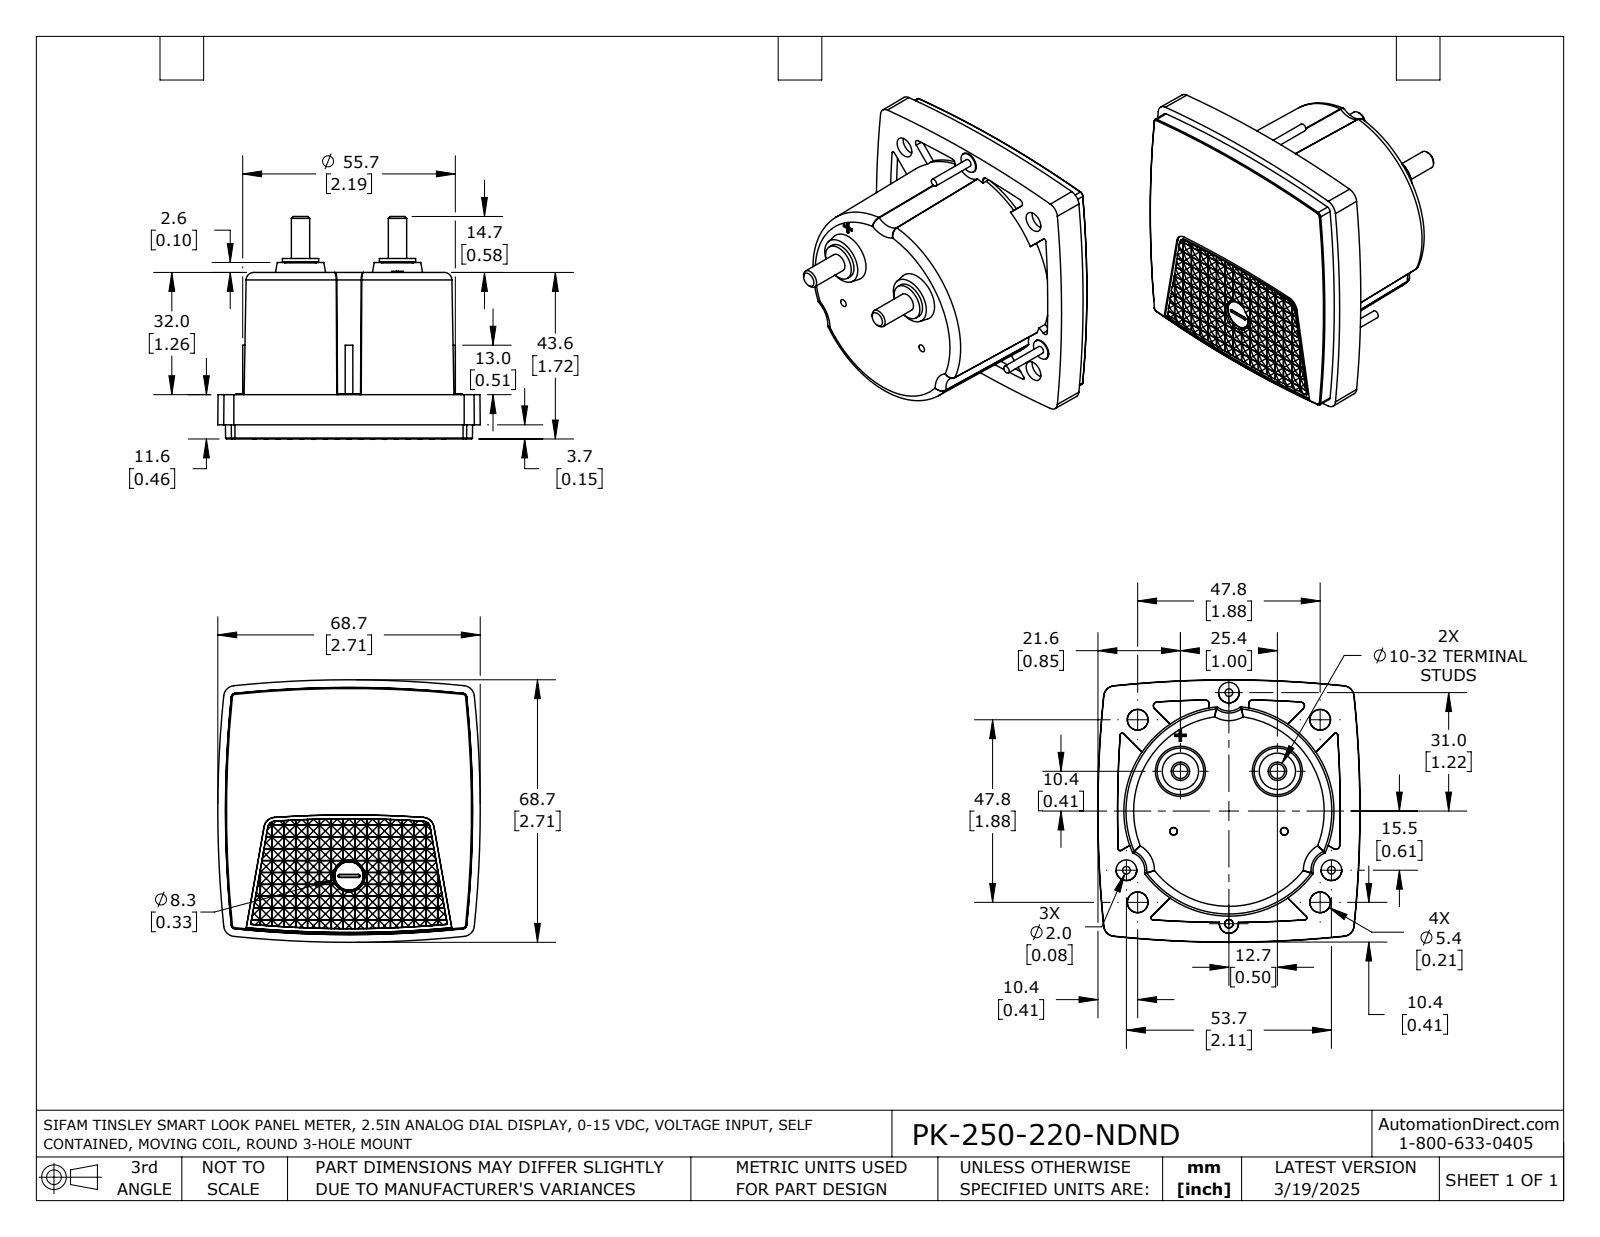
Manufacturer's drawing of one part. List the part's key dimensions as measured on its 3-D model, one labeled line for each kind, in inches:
Part name (STEP PRODUCT): PK-250-220-NDND
STEP written by: SolidWorks 2021 (AUTOMOTIVE_DESIGN)
Units: inches
Bodies: 1 solid, 1550 faces (1165 planar, 265 cylindrical, 120 other)
Overall size (bounding box): 2.706 × 2.706 × 2.297
Volume: 7.594 in³ · Surface area: 30.41 in²
Round bosses / shafts (diameter × count): ⌀0.213 ×3, ⌀0.079 ×3, ⌀0.374 ×2, ⌀0.189 ×2, ⌀0.215 ×1
Partial cylindrical surfaces — rounded edges, fillets, slot ends (radius × count): R0.167 ×2, R1.083 ×1
Main face-to-face distances: 1.717, 1.26, 0.457, 0.024, 0.087, 0.096, 0.311, 0.12, 0.072, 1.346
